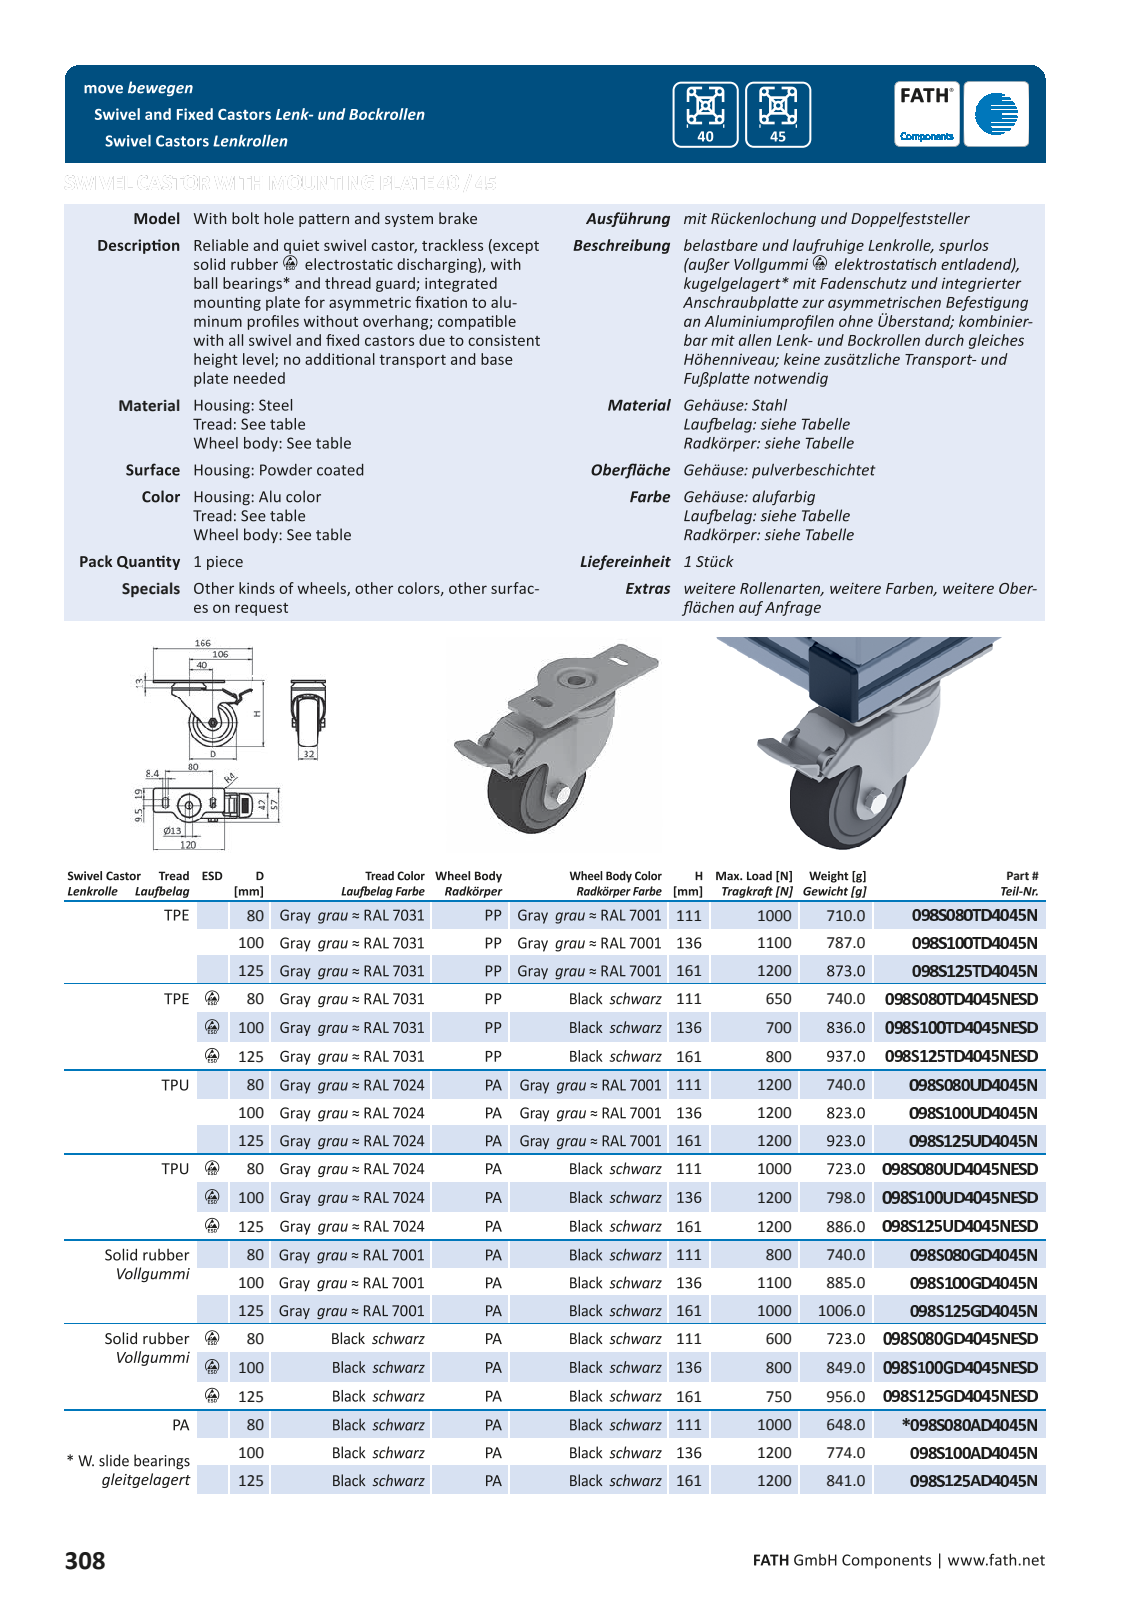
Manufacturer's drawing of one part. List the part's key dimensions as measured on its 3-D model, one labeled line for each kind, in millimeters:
Part name (STEP PRODUCT): Accessories for aluminium profiles098S100TD4045N; TPA_101_8K-FK_574202-214_selction no pls; 4DIN931M08048MS01; 4DIN934M08M (+1 more)
STEP written by: SolidWorks 2017 (AUTOMOTIVE_DESIGN)
Units: millimetres
Bodies: 5 solids, 1868 faces (855 planar, 353 cylindrical, 660 other)
Overall size (bounding box): 166.07 × 135.97 × 57
Volume: 342 498 mm³ · Surface area: 76 244 mm²
Round holes (diameter × count): ⌀8 ×1, ⌀8.5 ×1, ⌀12.5 ×1, ⌀13.44 ×1, ⌀38 ×1, ⌀39 ×1
Round bosses / shafts (diameter × count): ⌀70 ×1, ⌀57 ×1, ⌀55.51 ×1, ⌀41.2 ×1, ⌀20 ×1, ⌀13 ×1
Partial cylindrical surfaces — rounded edges, fillets, slot ends (radius × count): R0.8 ×84, R0.6 ×16, R1 ×14, R1.25 ×14, R1.65 ×14, R0.9 ×12, R1.5 ×10, R4 ×10
Main face-to-face distances: 2.5, 3, 39.5, 37, 3.5, 36, 42, 1, 38.5, 1.5
